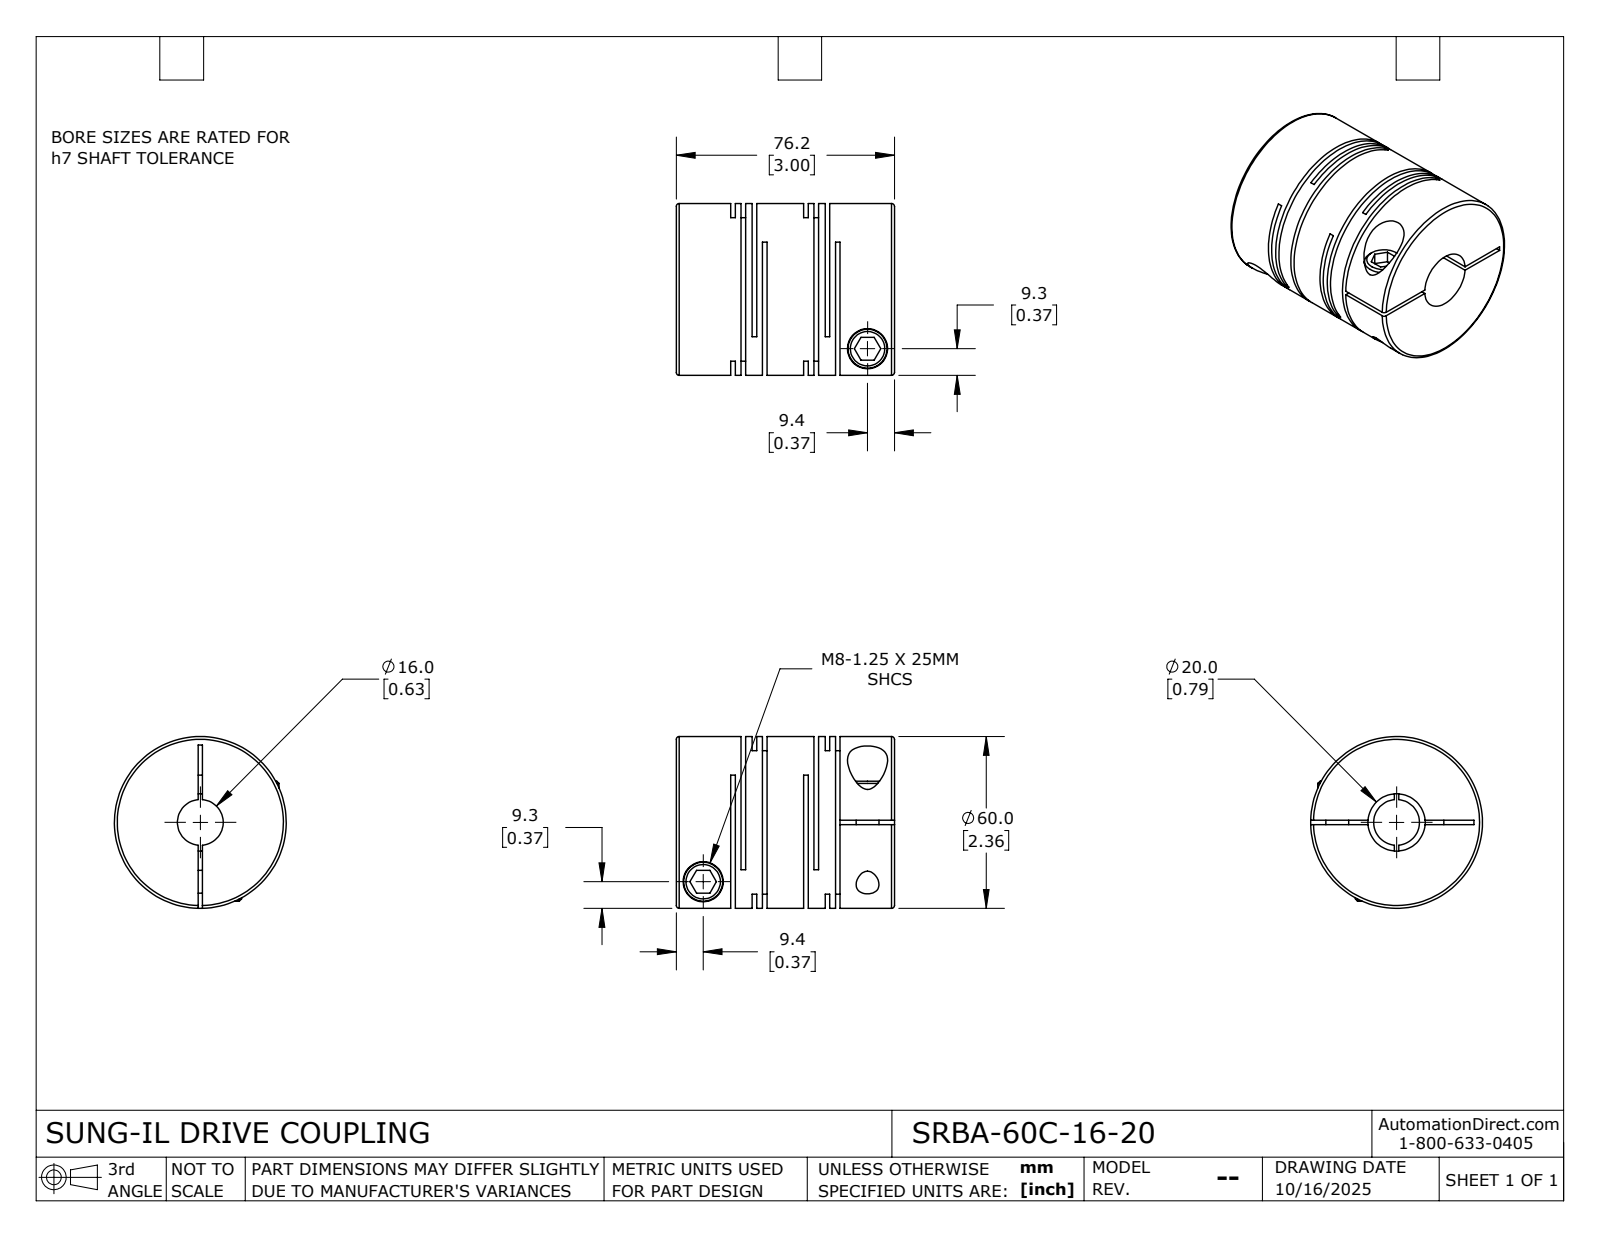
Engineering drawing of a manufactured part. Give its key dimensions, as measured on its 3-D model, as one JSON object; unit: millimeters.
{"part_name": "SRBA-60C-16-20", "step_written_by": "SolidWorks 2024 (CONFIG_CONTROL_DESIGN)", "units": "millimeters", "bodies": {"solids": 1, "faces": 115, "planar": 60, "cylindrical": 42, "other": 13}, "overall_size": [76.2, 60, 60], "volume_mm3": 162313, "surface_area_mm2": 59249, "round_holes": [[8, 2], [14, 2], [16, 1], [20, 1]], "round_bosses_or_shafts": [[13.6, 2], [60, 1]], "face_to_face_distances": [1.6, 3.6, 7.5, 25.5, 33, 2, 5.9, 23.9, 3.9, 18]}
